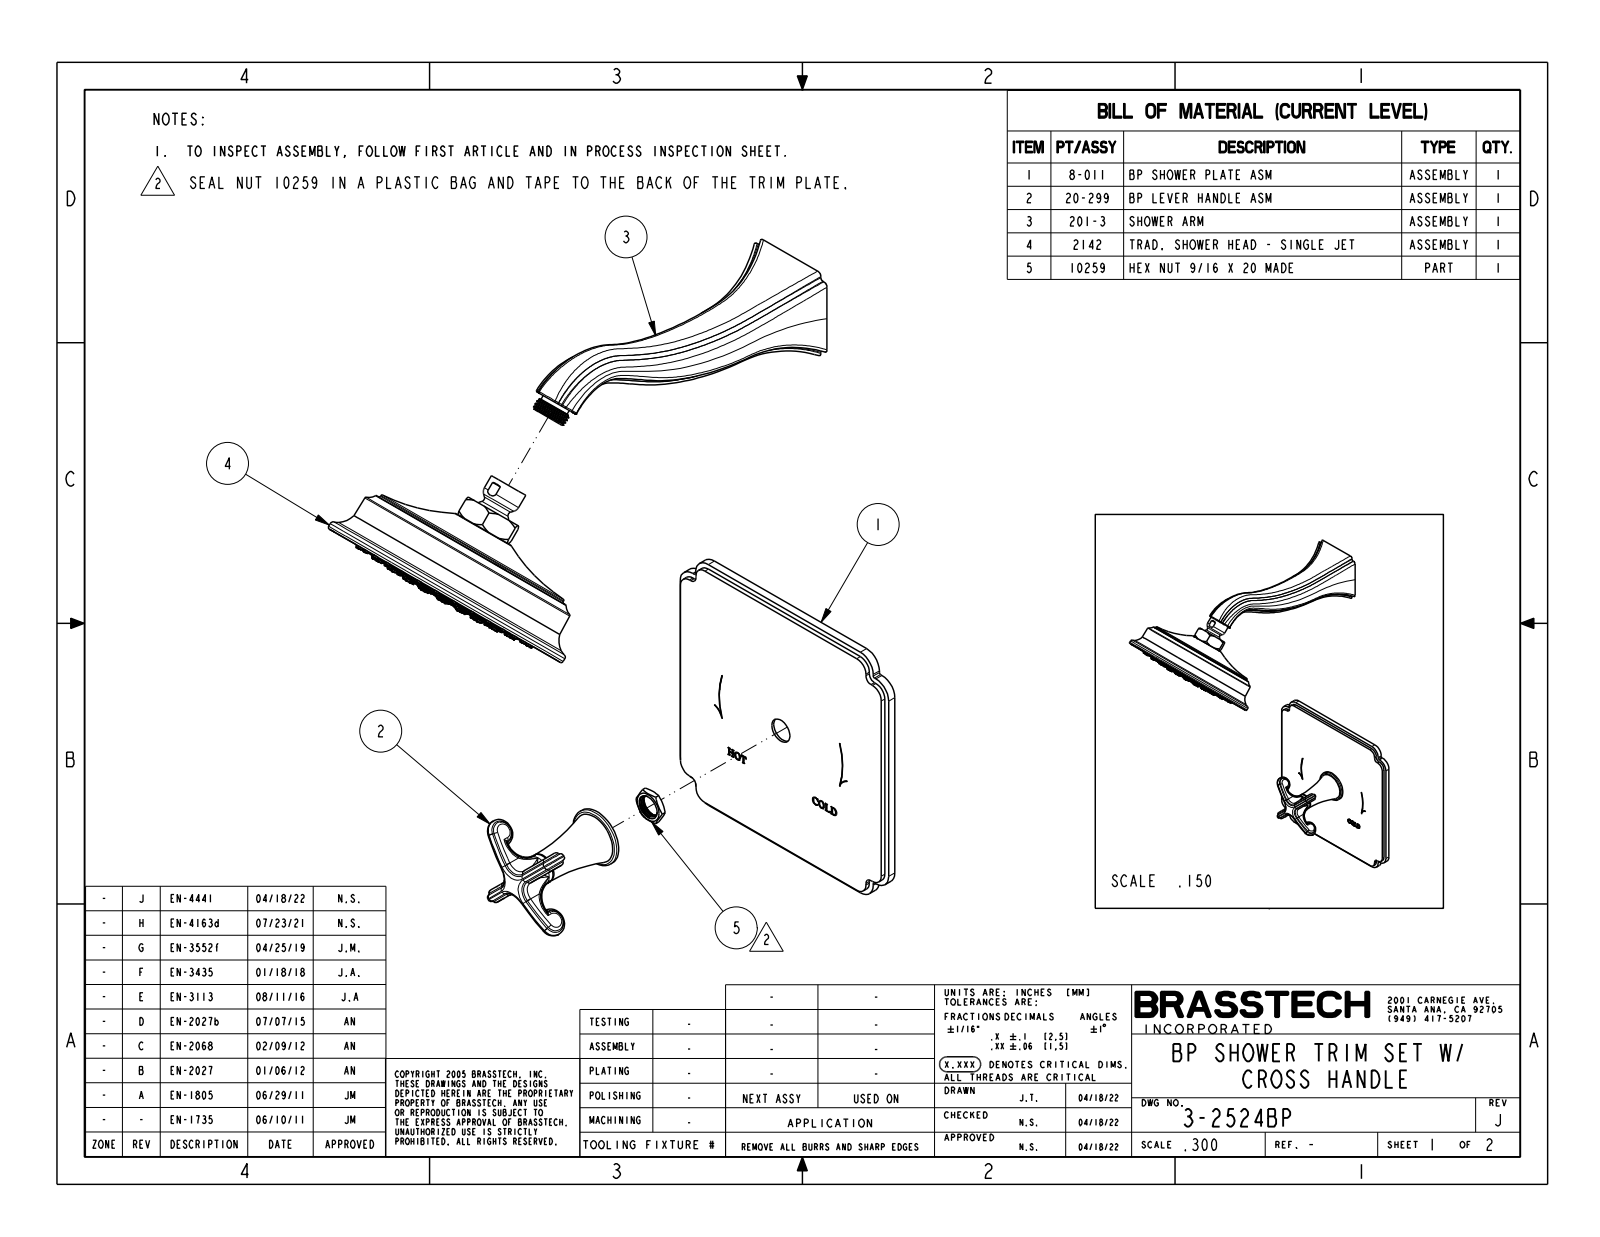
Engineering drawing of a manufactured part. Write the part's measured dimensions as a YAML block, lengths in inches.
part_name: "3-2524BP"
step_written_by: "CREO PARAMETRIC BY PTC INC, 2018400 (AUTOMOTIVE_DESIGN)"
units: inches
bodies: {solids: 64, faces: 2015, planar: 529, cylindrical: 640, other: 846}
overall_size: [17.052, 12.053, 6.75]
volume: 58.53
surface_area: 304.2
round_holes:
  - {diameter: 0.05, count: 90}
  - {diameter: 0.125, count: 90}
  - {diameter: 0.22, count: 1}
  - {diameter: 0.59, count: 1}
  - {diameter: 0.604, count: 1}
  - {diameter: 2, count: 1}
  - {diameter: 4.9, count: 1}
  - {diameter: 5.7, count: 1}
  - {diameter: 6.25, count: 1}
round_bosses_or_shafts:
  - {diameter: 0.198, count: 90}
  - {diameter: 6.2, count: 2}
  - {diameter: 5.5, count: 1}
  - {diameter: 5.22, count: 1}
  - {diameter: 4.83, count: 1}
  - {diameter: 2, count: 1}
  - {diameter: 1.42, count: 1}
  - {diameter: 1.4, count: 1}
partial_cylinders:
  - {radius: 0.04, count: 20}
  - {radius: 0.07, count: 8}
  - {radius: 0.29, count: 8}
  - {radius: 0.415, count: 8}
  - {radius: 0.165, count: 4}
  - {radius: 0.318, count: 4}
  - {radius: 0.394, count: 2}
  - {radius: 0.404, count: 2}
face_to_face_distances: [0.313, 0.05, 0.25, 0.2, 0.113, 0.363, 0.04, 0.21, 0.323, 0.3]
hole_center_spacings: [1.84, 0.48, 3.648, 1.84, 2.24, 2.919, 3.555, 1.408]
